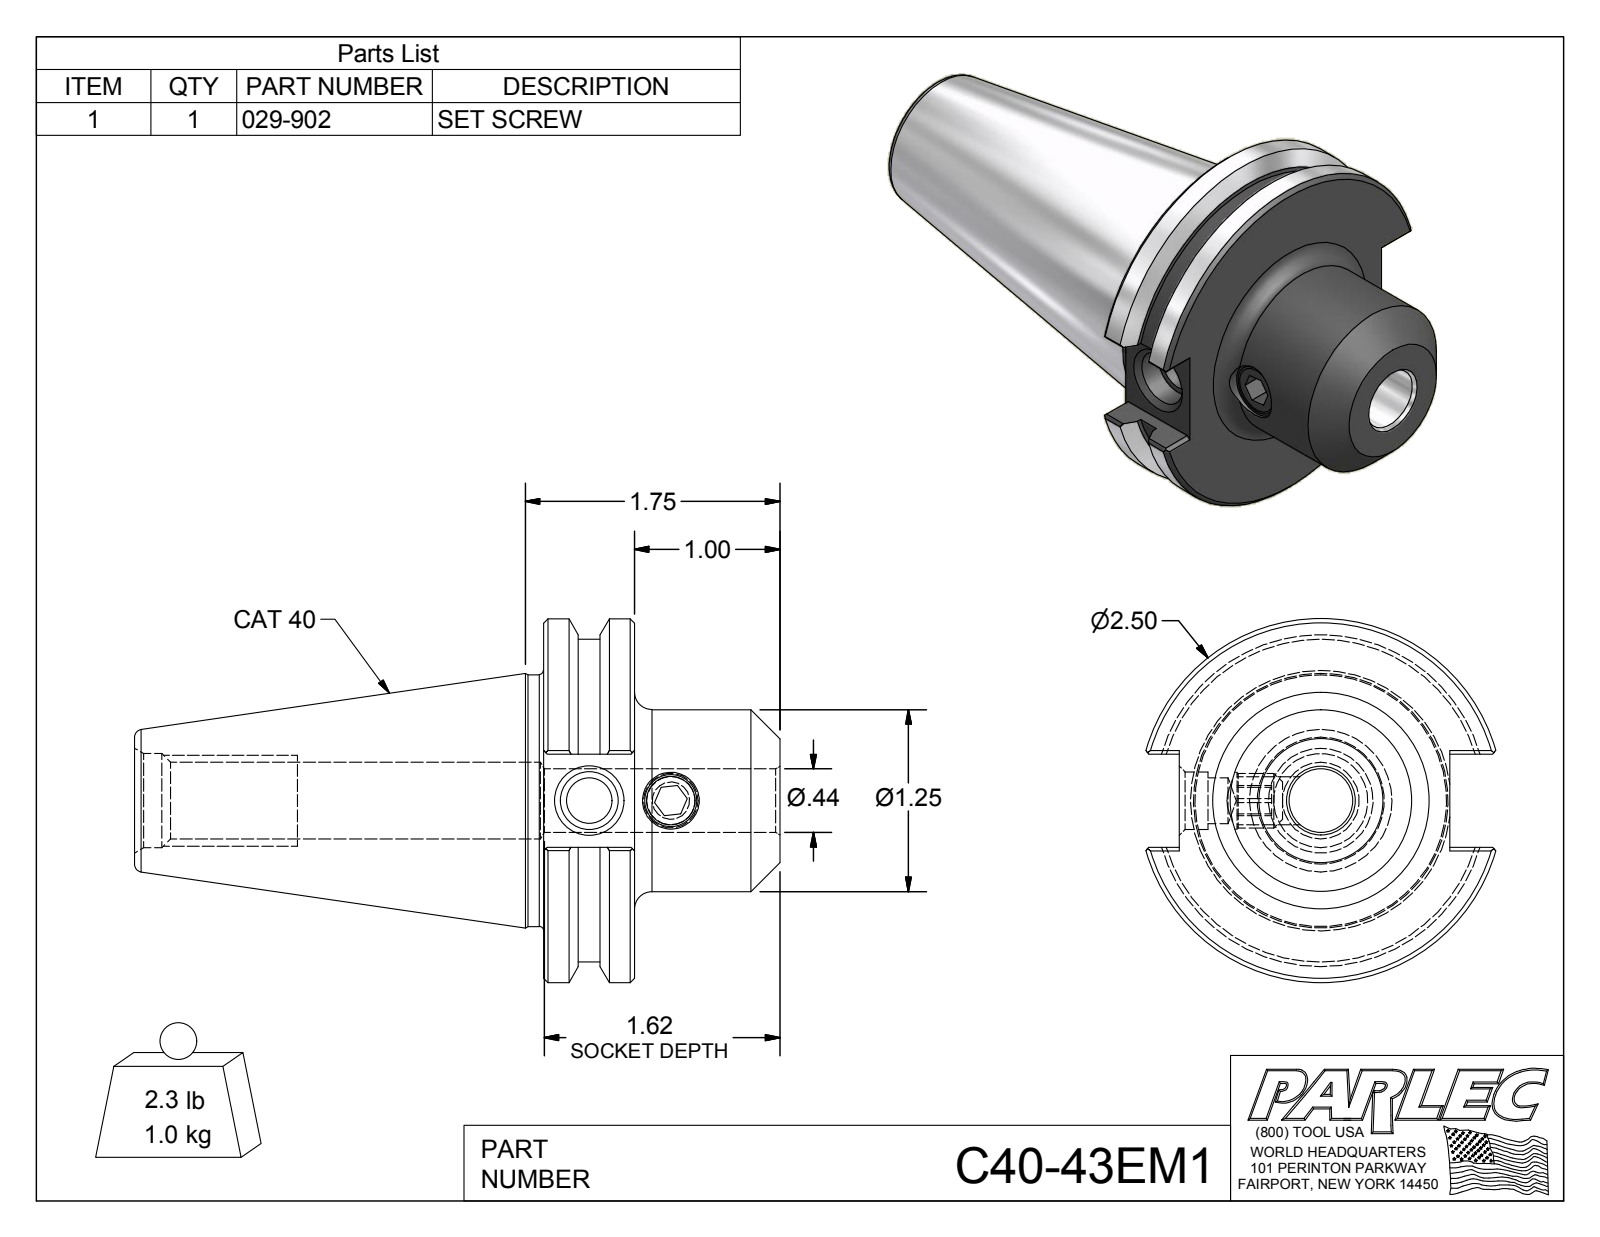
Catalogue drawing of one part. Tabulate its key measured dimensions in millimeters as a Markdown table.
| quantity | value |
| --- | --- |
| part name | C40-43EM1; C40-43EM1-1; 029-902 |
| STEP written by | Autodesk Inventor 2012 (AUTOMOTIVE_DESIGN) |
| units | millimeters |
| bodies | 2 solids, 79 faces (41 planar, 16 cylindrical, 22 other) |
| overall size | 112.7 × 63.5 × 61 |
| volume | 117 500 mm³ |
| surface area | 23 730 mm² |
| round holes (diameter × count) | 8 × 1, 8.4 × 1, 9.9 × 1, 10.1 × 1, 11.1 × 1, 13.4 × 1, 16.5 × 1 |
| round bosses / shafts (diameter × count) | 63.5 × 1, 56.4 × 1, 43.9 × 1, 31.8 × 1, 9.5 × 1 |
| main face-to-face distances | 15.9, 41.3, 25.4, 16.3, 47.2, 6, 71.5, 87.3, 112.7, 81.3 |
| hole center spacings | 14.2 |
